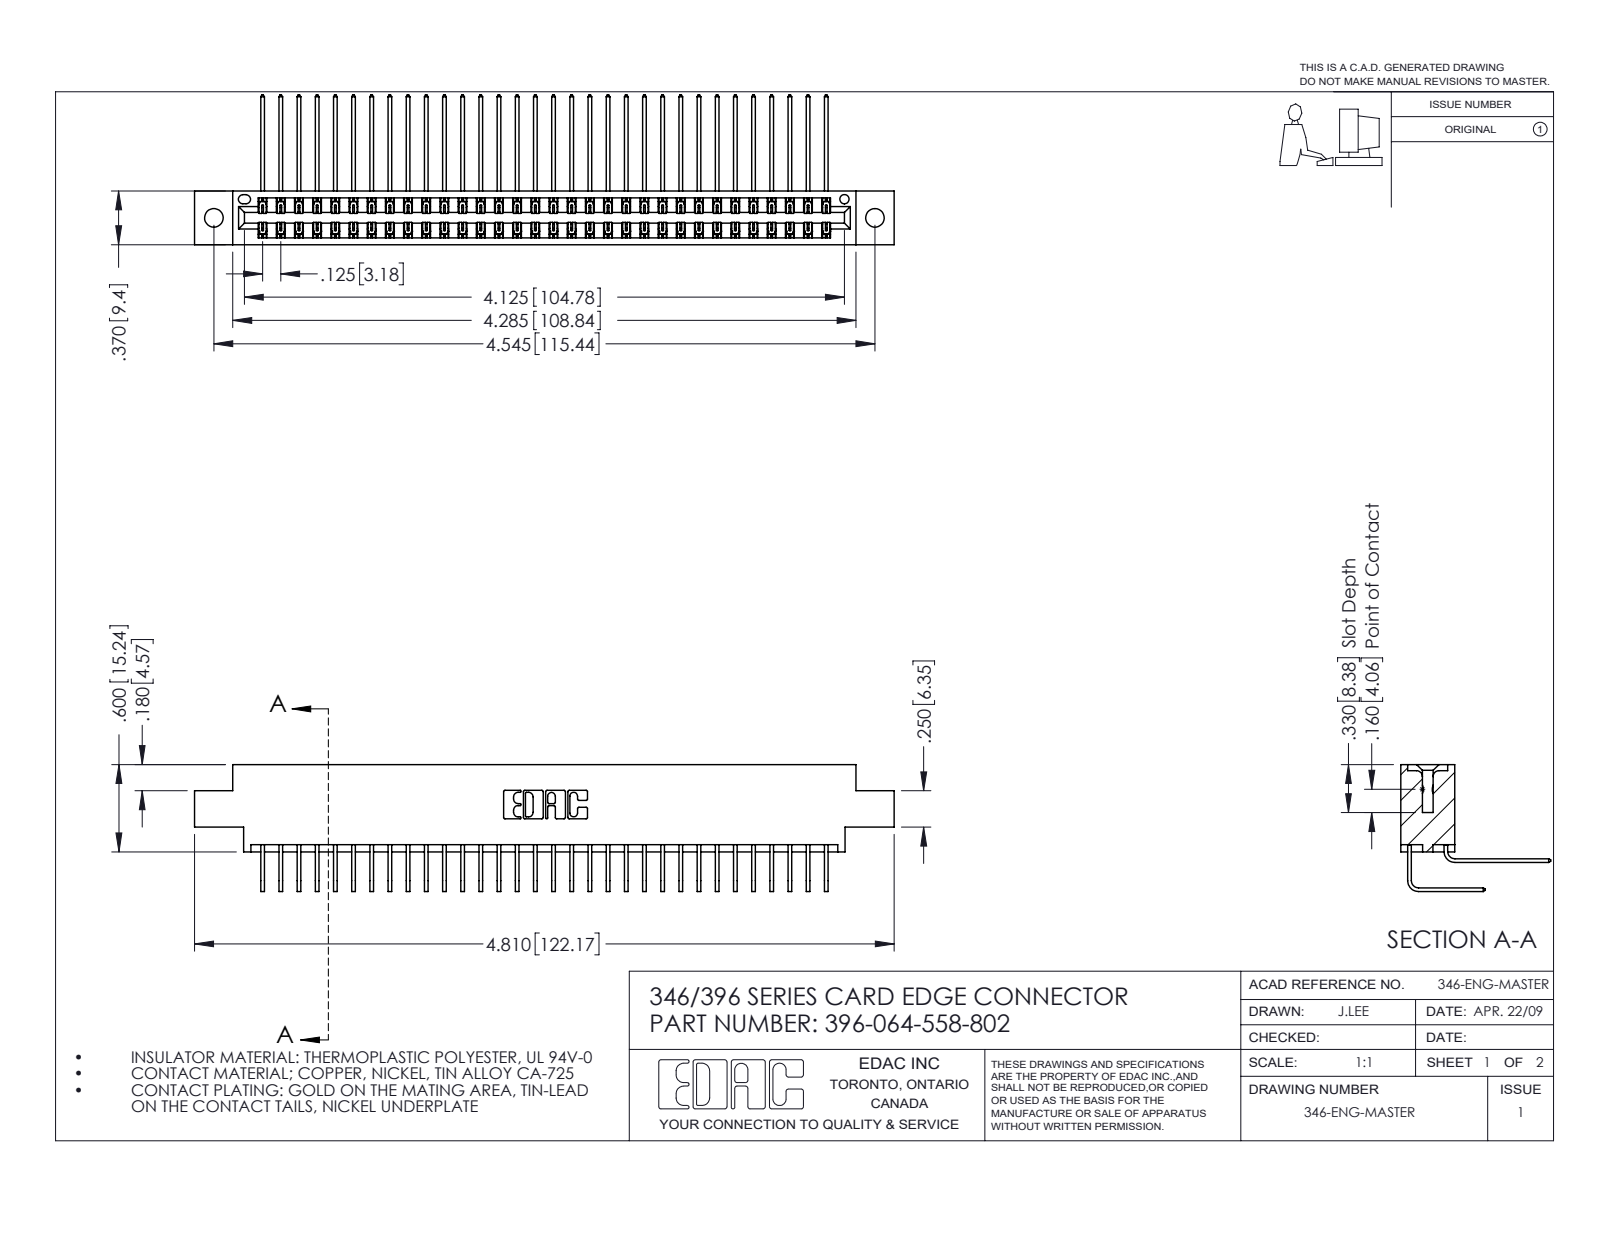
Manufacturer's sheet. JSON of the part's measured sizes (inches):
{"part_name": "345-292-001_558 559 Tail - 1; 396-064-558-802; 345-292-001_558 Tail - 2; 346 Part_0.170 Offset - 0.128 Dia", "step_written_by": "SolidWorks 2016 (CONFIG_CONTROL_DESIGN)", "units": "inches", "bodies": {"solids": 65, "faces": 3582, "planar": 2448, "cylindrical": 1134, "other": 0}, "overall_size": [4.81, 1.03, 0.873], "volume_in3": 0.733, "surface_area_in2": 27.96, "round_holes": [[0.128, 2], [0.064, 1]], "partial_cylinders_radius": [[0.006, 96], [0.01, 22], [0.007, 6], [0.031, 6], [0.026, 3], [0.014, 2], [0.022, 2], [0.024, 2]], "face_to_face_distances": [0.322, 0.048, 0.025, 0.37, 0.25, 0.298, 0.072, 0.275, 0.148, 0.222], "hole_center_spacings": [0.246, 4.337, 4.545]}
